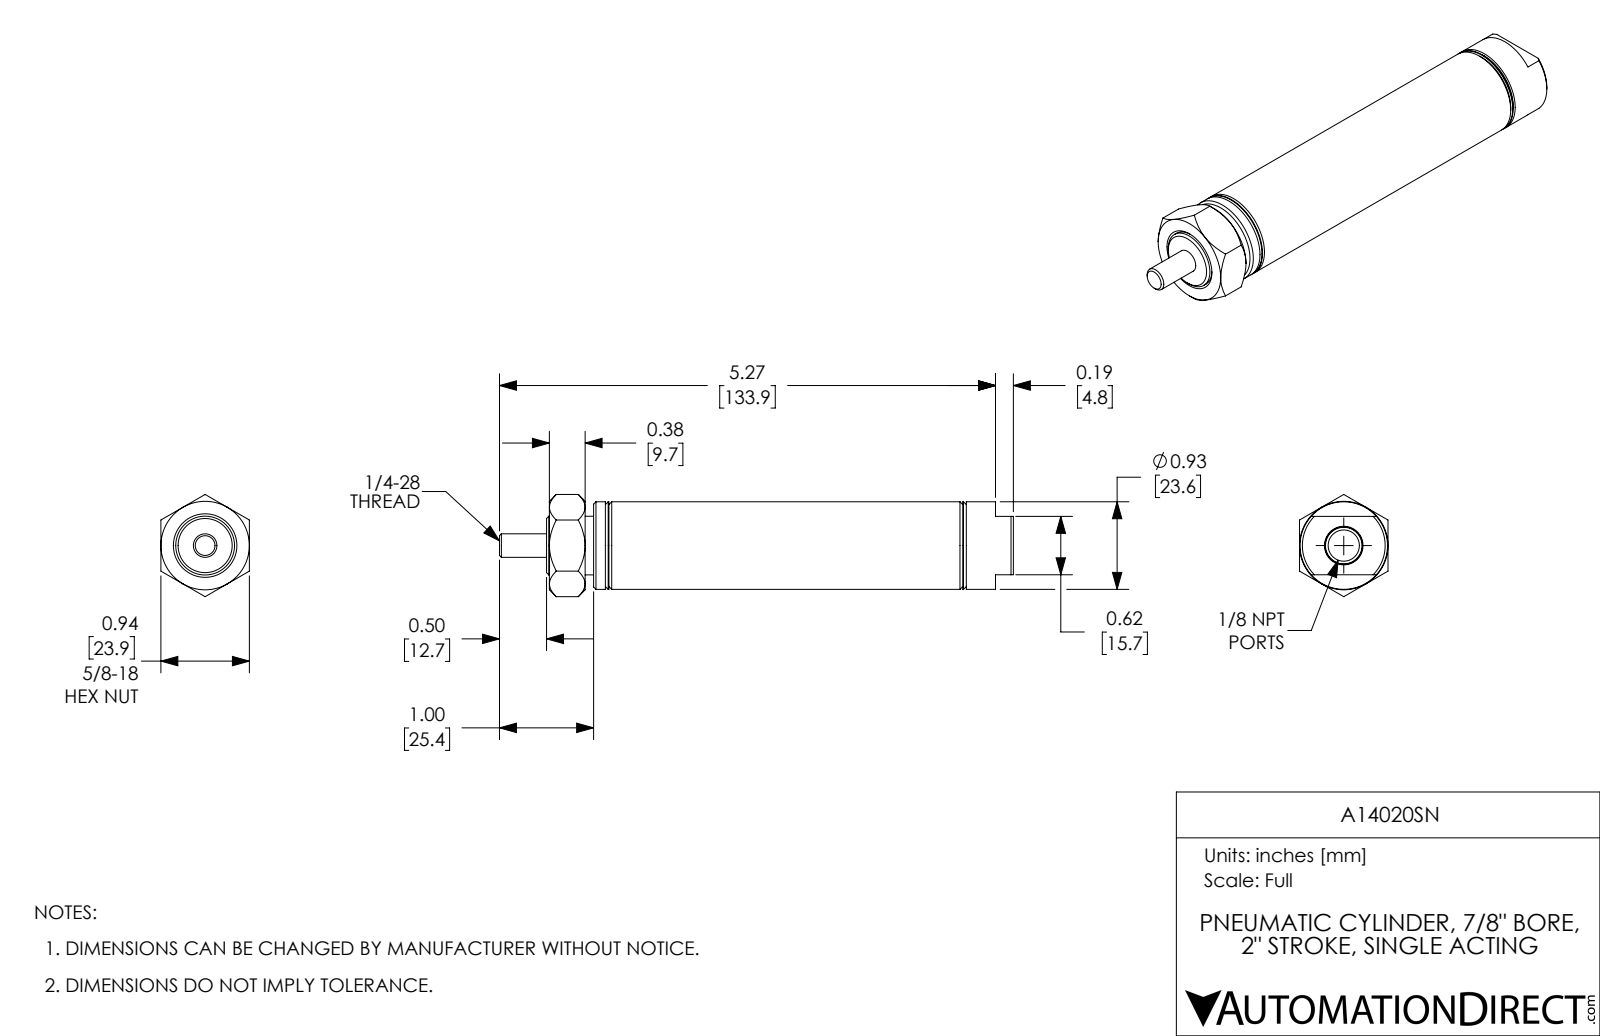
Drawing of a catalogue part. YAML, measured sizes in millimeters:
part_name: "A14020SN; A14020SN_Mounting Nut_D-9; A14020SN_Rod; A14020SN_Main Body"
step_written_by: "SolidWorks 2017 (AUTOMOTIVE_DESIGN)"
units: millimeters
bodies: {solids: 3, faces: 94, planar: 27, cylindrical: 28, other: 39}
overall_size: [138.7, 27.6, 23.9]
volume: 36250
surface_area: 21480
round_holes:
  - {diameter: 6.4, count: 1}
  - {diameter: 8.4, count: 1}
  - {diameter: 15.9, count: 1}
  - {diameter: 22.2, count: 1}
round_bosses_or_shafts:
  - {diameter: 23.6, count: 1}
  - {diameter: 15.8, count: 1}
  - {diameter: 14.3, count: 1}
face_to_face_distances: [12.7, 63.5, 50.8, 23.9, 83.6, 29.6, 85.9, 73.2, 22.4, 113.3]
